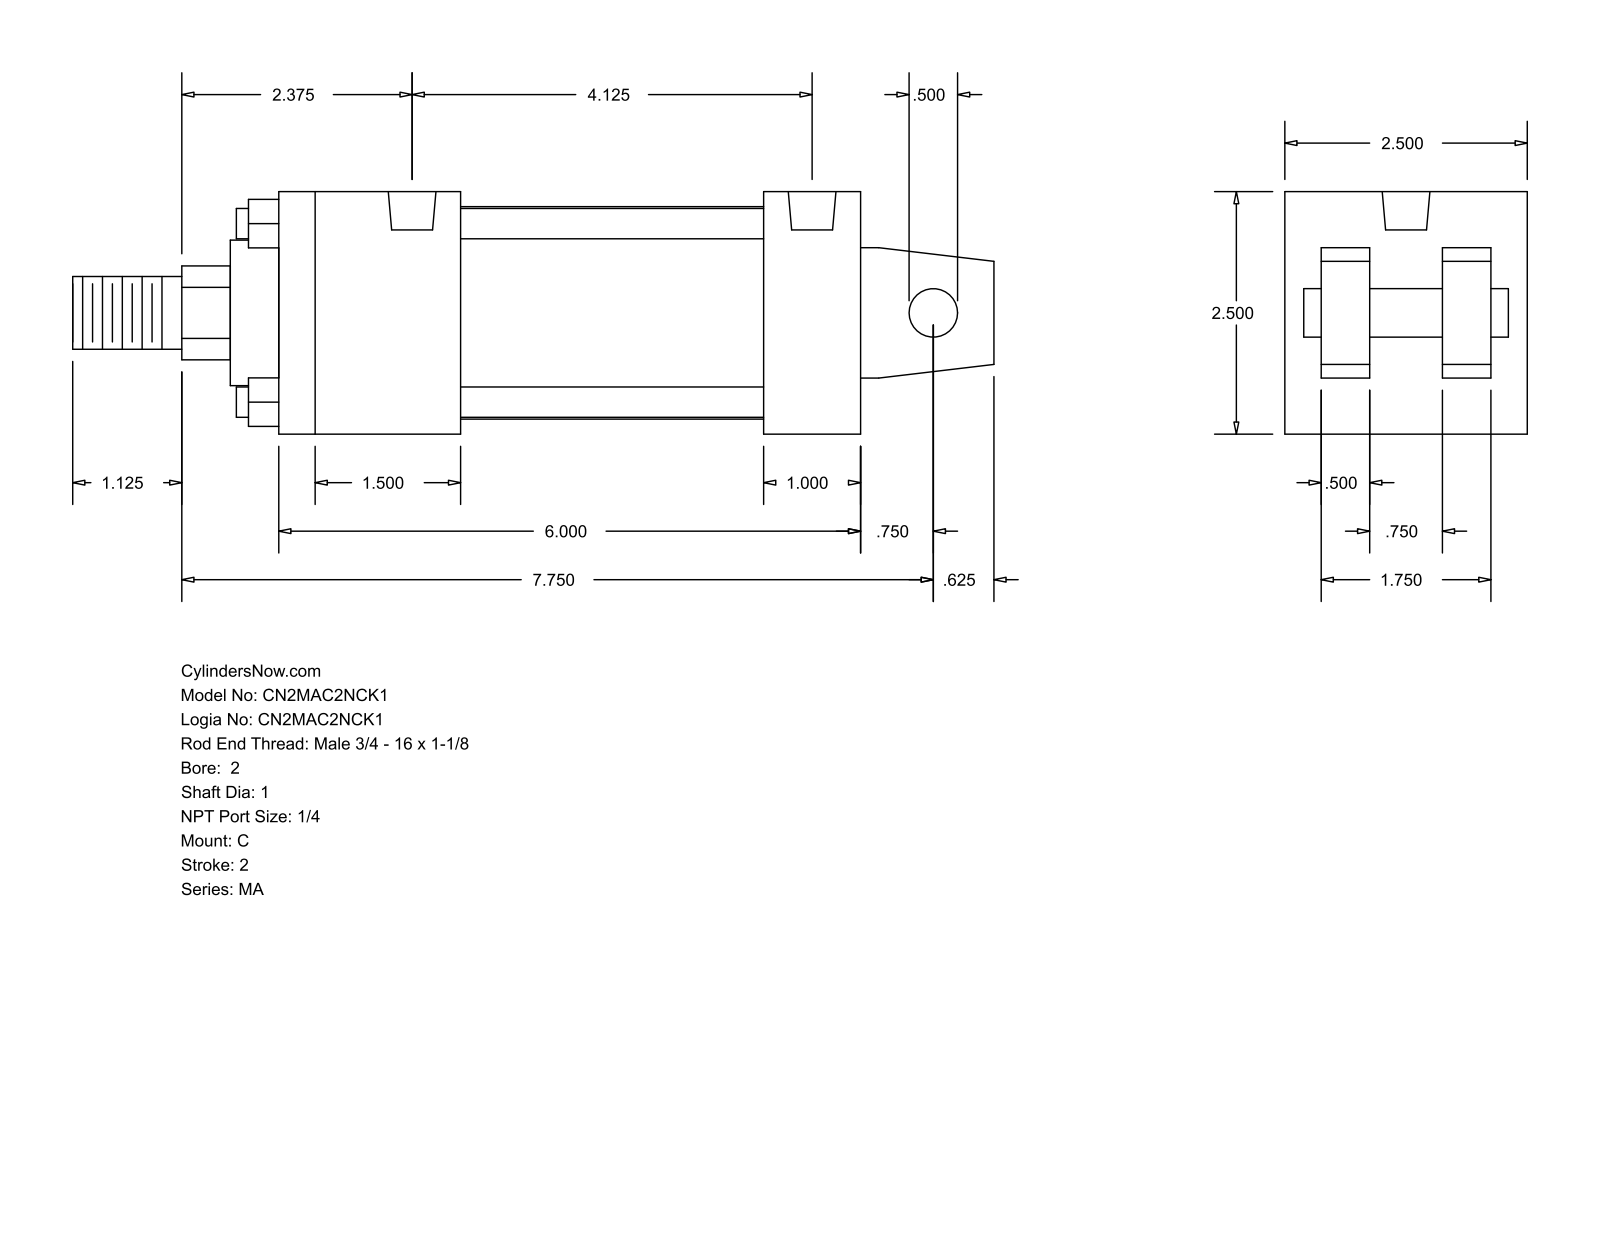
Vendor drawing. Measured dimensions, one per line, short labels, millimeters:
name: MA_C__0200_1
written by: GSSL Pune (CONFIG_CONTROL_DESIGN)
unit: mm
bodies: 0 solids, 103 faces (76 planar, 27 cylindrical, 0 other)
size: 241.3 × 63.5 × 63.5
holes: 4× ⌀7.94, 2× ⌀12.49
bosses: 4× ⌀7.94, 1× ⌀55.63, 1× ⌀38.1, 1× ⌀25.4, 1× ⌀19.05, 1× ⌀12.7
rounds: 1× R12.29
face distances: 63.5, 12.7, 152.4, 22.22, 41.28, 9.52, 53.98, 31.76, 47.63, 25.4
hole spacings: 104.77
